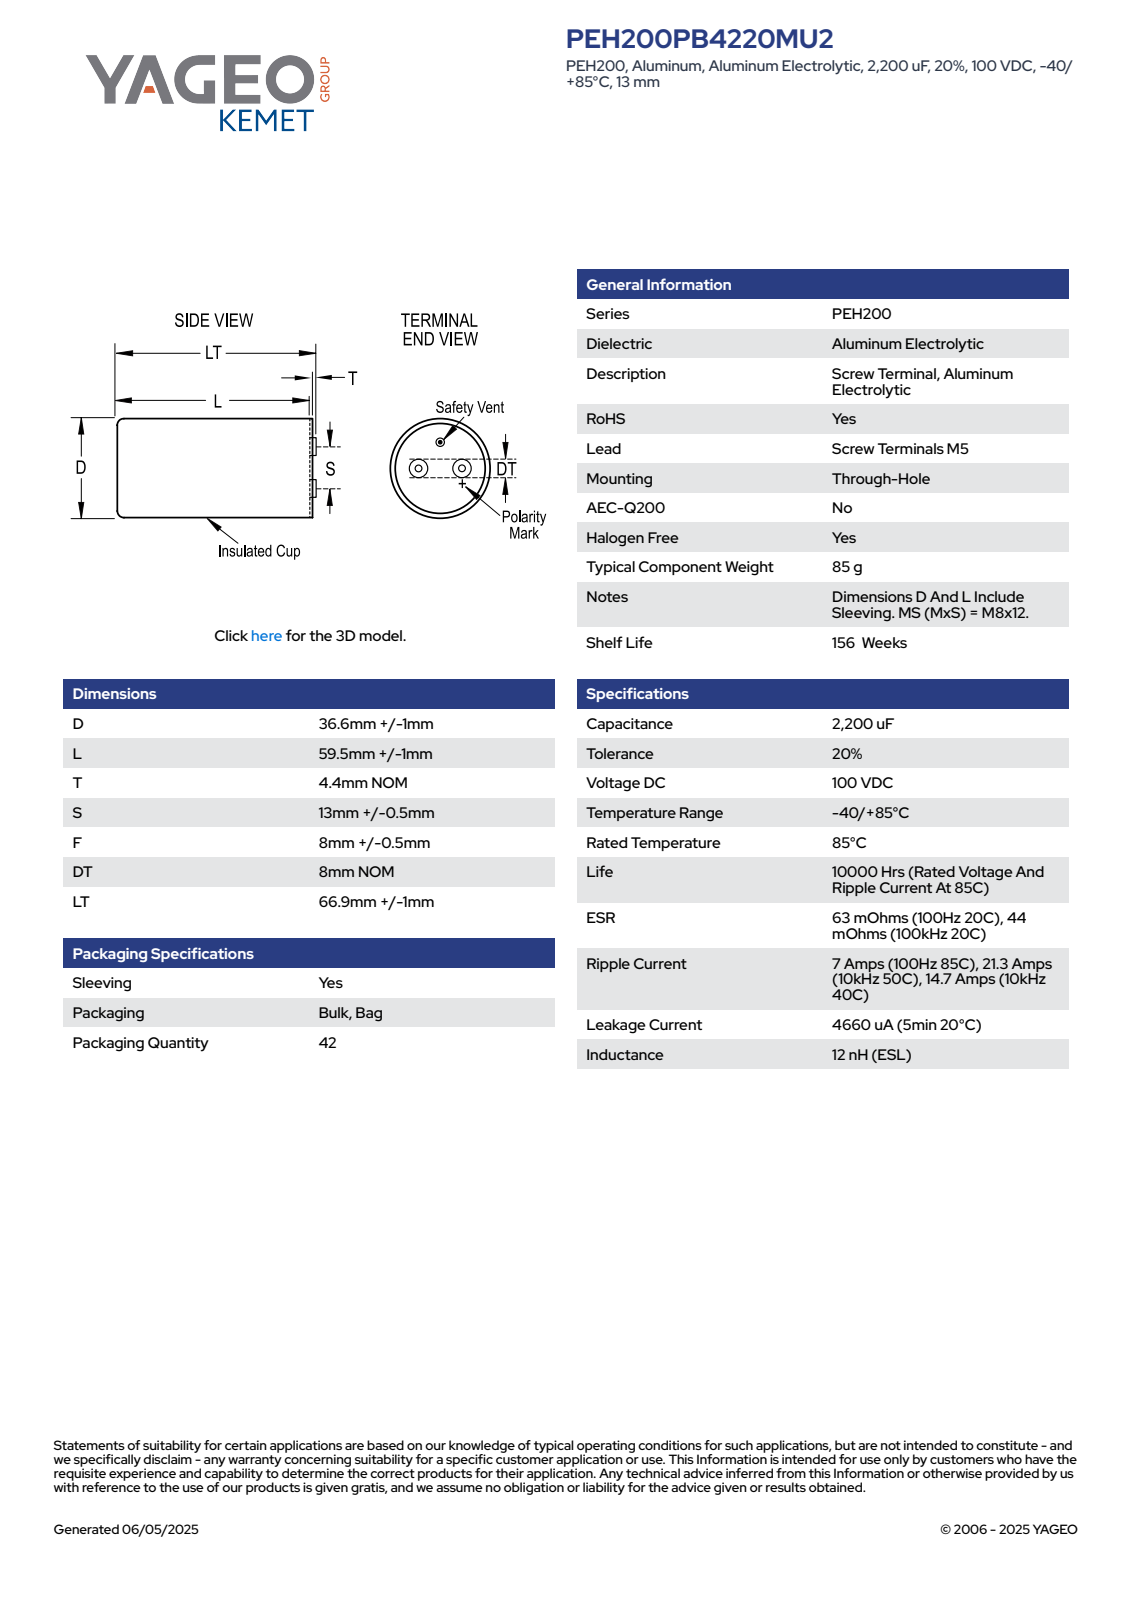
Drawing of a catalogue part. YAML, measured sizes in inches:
part_name: "Round_Terminal; CARC_D37.6L60.5S13T4.4; Can_Round_2"
step_written_by: "SolidWorks 2014 (AUTOMOTIVE_DESIGN)"
units: inches
bodies: {solids: 3, faces: 77, planar: 30, cylindrical: 15, other: 32}
overall_size: [2.673, 1.48, 1.48]
volume: 4.124
surface_area: 16.39
round_holes:
  - {diameter: 0.197, count: 2}
  - {diameter: 1.402, count: 1}
round_bosses_or_shafts:
  - {diameter: 0.315, count: 2}
  - {diameter: 1.48, count: 1}
partial_cylinders:
  - {radius: 0.74, count: 1}
face_to_face_distances: [2.382, 0.118, 2.5, 0.173, 0.291, 2.673, 0.689, 0.516, 0.398, 1.984]
hole_center_spacings: [0.256, 0.512]
